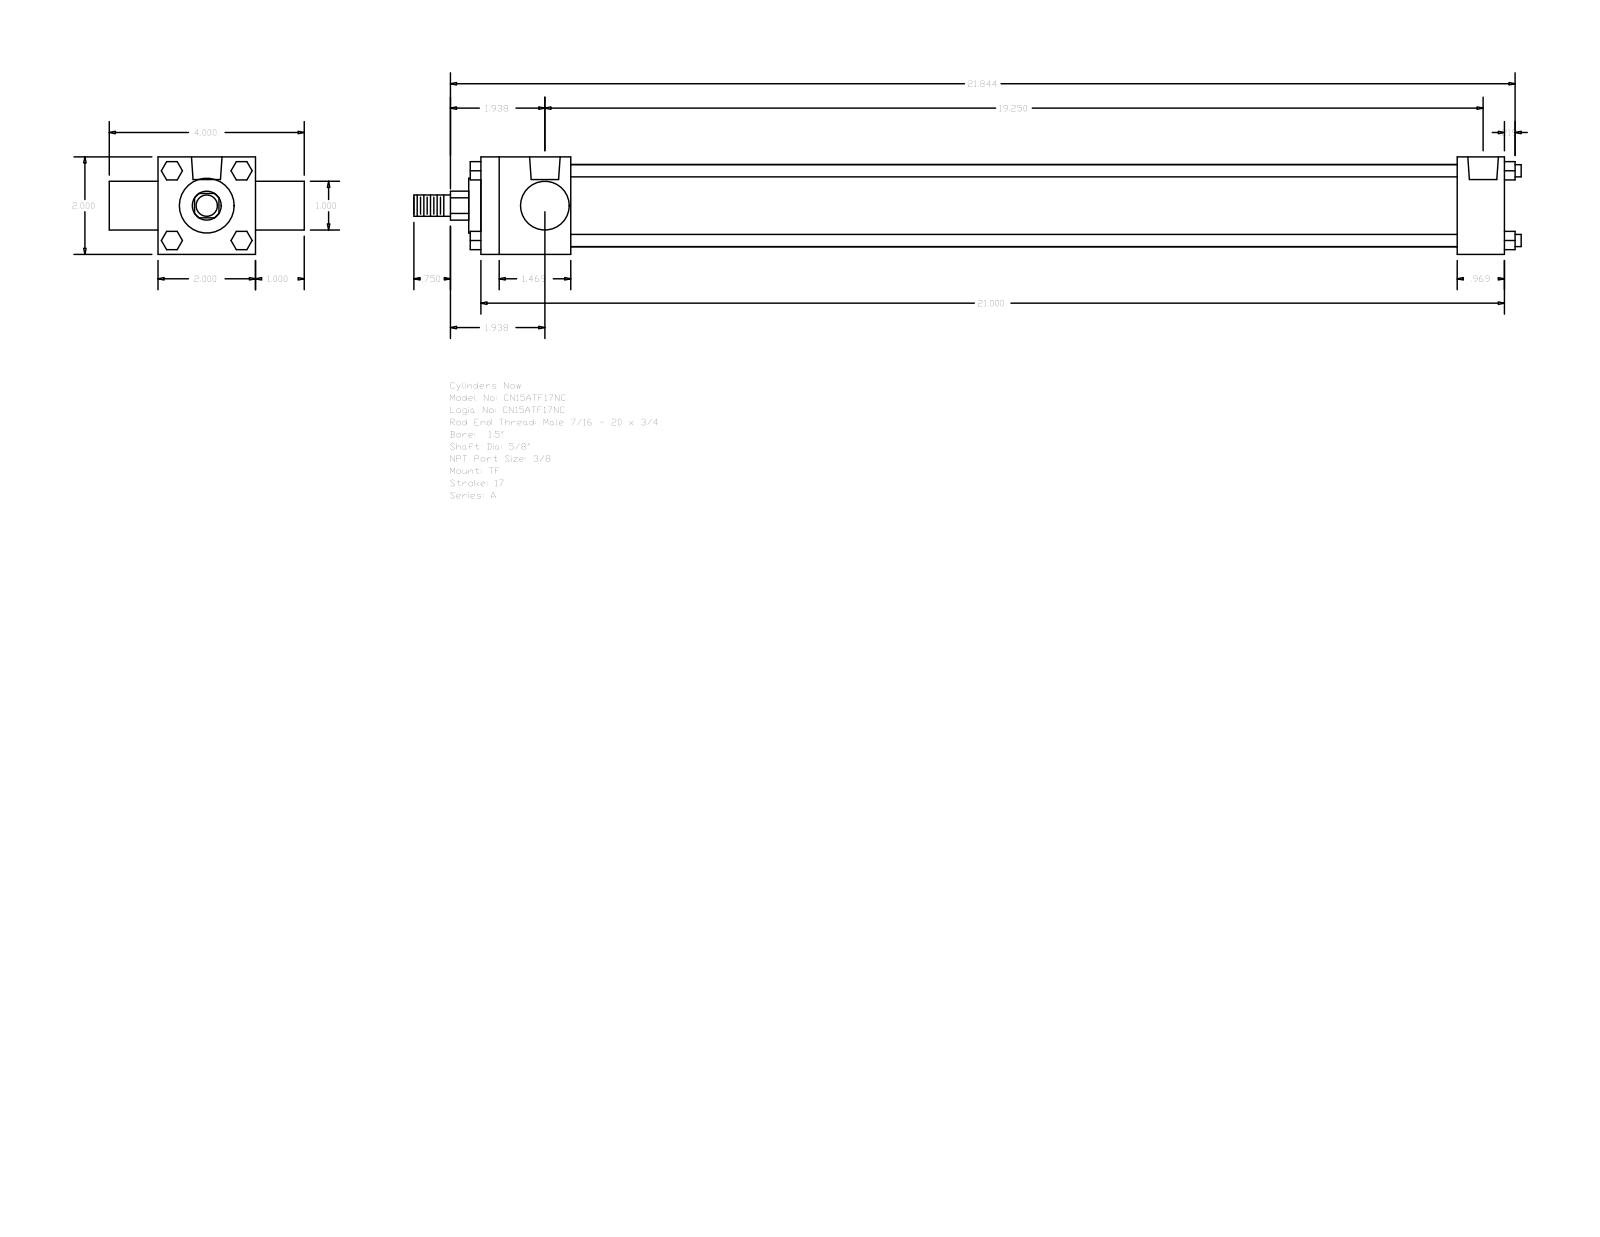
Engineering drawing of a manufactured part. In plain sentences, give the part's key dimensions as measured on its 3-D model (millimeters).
The part is named "A_TF__0150_0.625". Its 3-D file was written by "GSSL Pune (CONFIG_CONTROL_DESIGN)". It is 0 solids with 120 faces: 92 planar, 28 cylindrical and 0 other. Overall it measures 577.06 by 101.6 by 50.8 millimeters. Round holes: 3 of diameter 5.56, 2 of diameter 15.93. Round bosses or shafts: 4 of diameter 6.35, 1 of diameter 42.93, 1 of diameter 28.57, 1 of diameter 25.4, 1 of diameter 15.88, 1 of diameter 11.11. Partial cylindrical surfaces (rounded edges, fillets, slot ends): 1 of radius 7.54. The main face-to-face distances are 50.8, 533.39, 25.4, 76.2, 46.83, 508.79, 461.96, 486.56, 24.6, 101.6. The hole center spacings are 3.97, 484.98, 481.01, 488.95.
